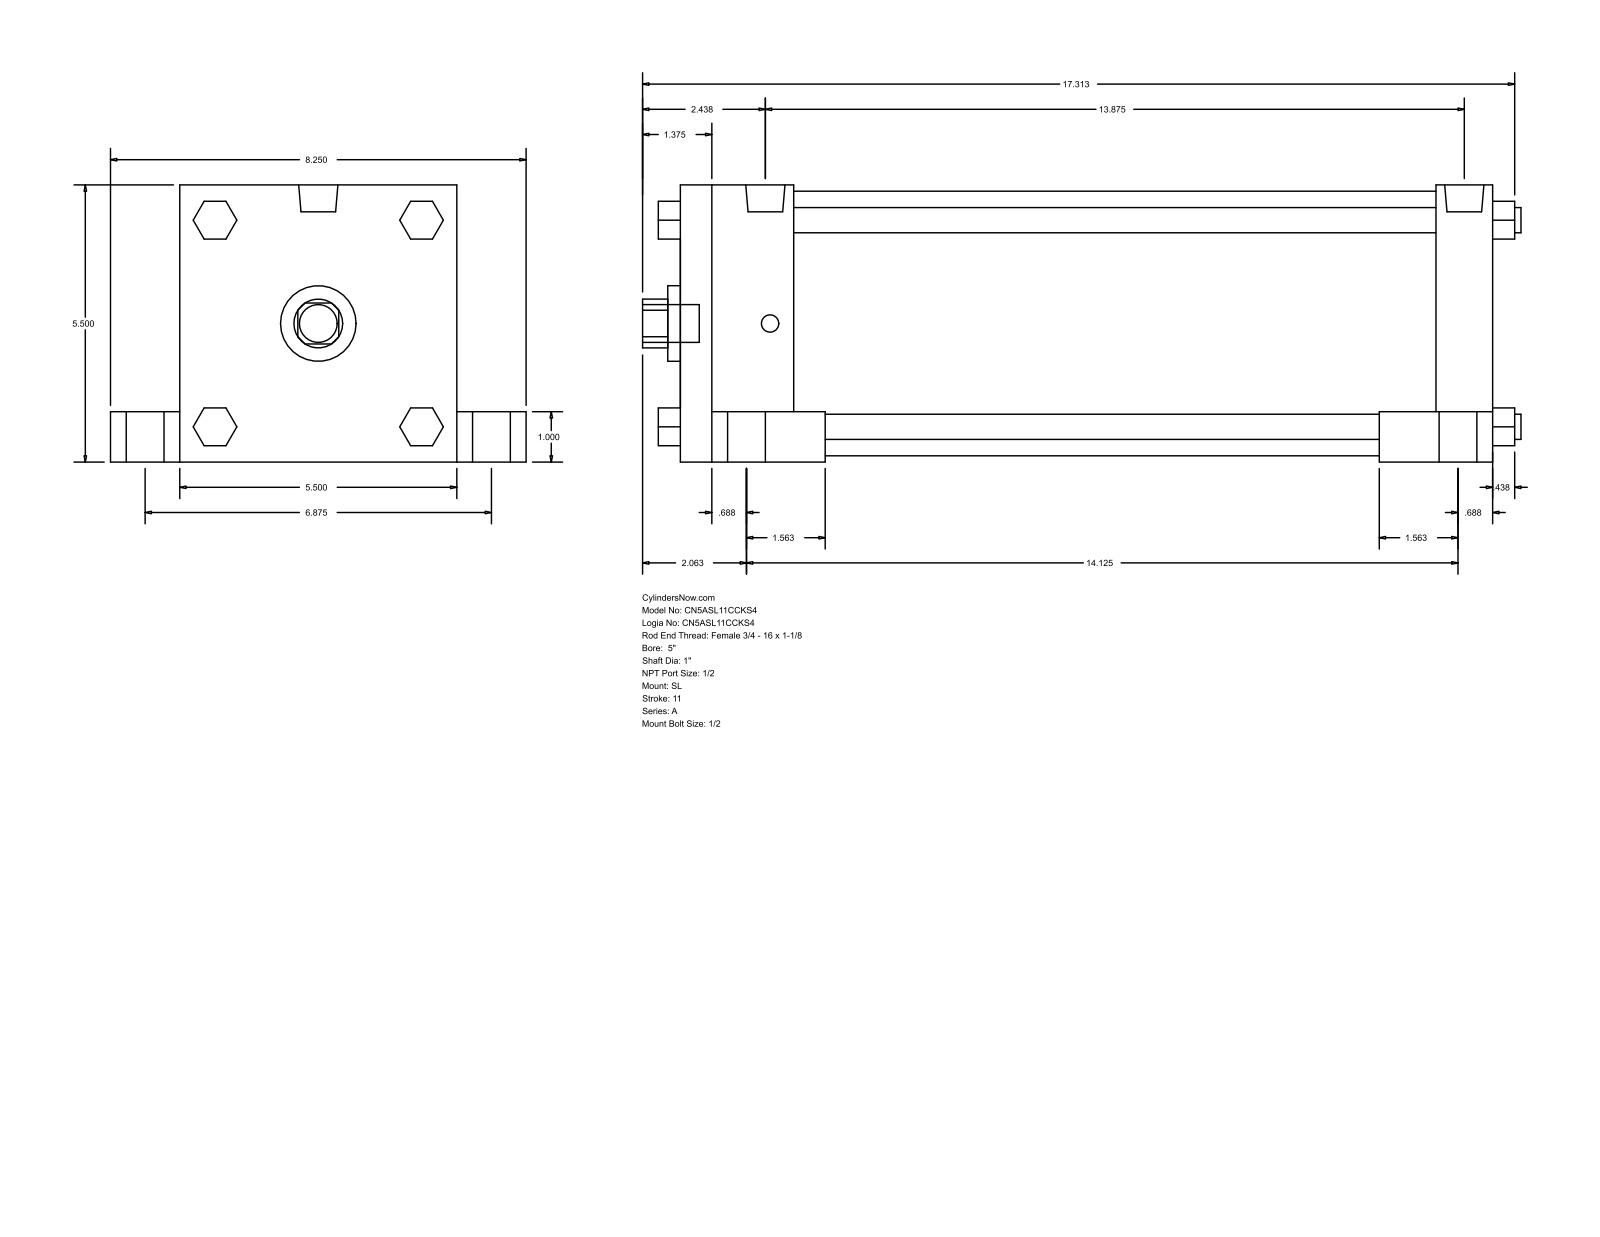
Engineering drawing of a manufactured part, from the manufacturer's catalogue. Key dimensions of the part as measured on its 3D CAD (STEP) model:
Part name (STEP PRODUCT): A_SL__0500_1
STEP written by: GSSL Pune (CONFIG_CONTROL_DESIGN)
Units: millimetres
Bodies: 0 solids, 150 faces (114 planar, 36 cylindrical, 0 other)
Overall size (bounding box): 442.91 × 209.55 × 139.7
Round holes (diameter × count): ⌀25.4 ×1, ⌀38.1 ×1, ⌀133.35 ×1
Round bosses / shafts (diameter × count): ⌀19.05 ×5, ⌀25.4 ×4, ⌀12.7 ×4, ⌀8.73 ×4, ⌀19.77 ×2
Partial cylindrical surfaces — rounded edges, fillets, slot ends (radius × count): R12.29 ×1
Main face-to-face distances: 139.7, 409.57, 28.57, 25.4, 114.3, 34.93, 174.63, 57.15, 381, 323.85
